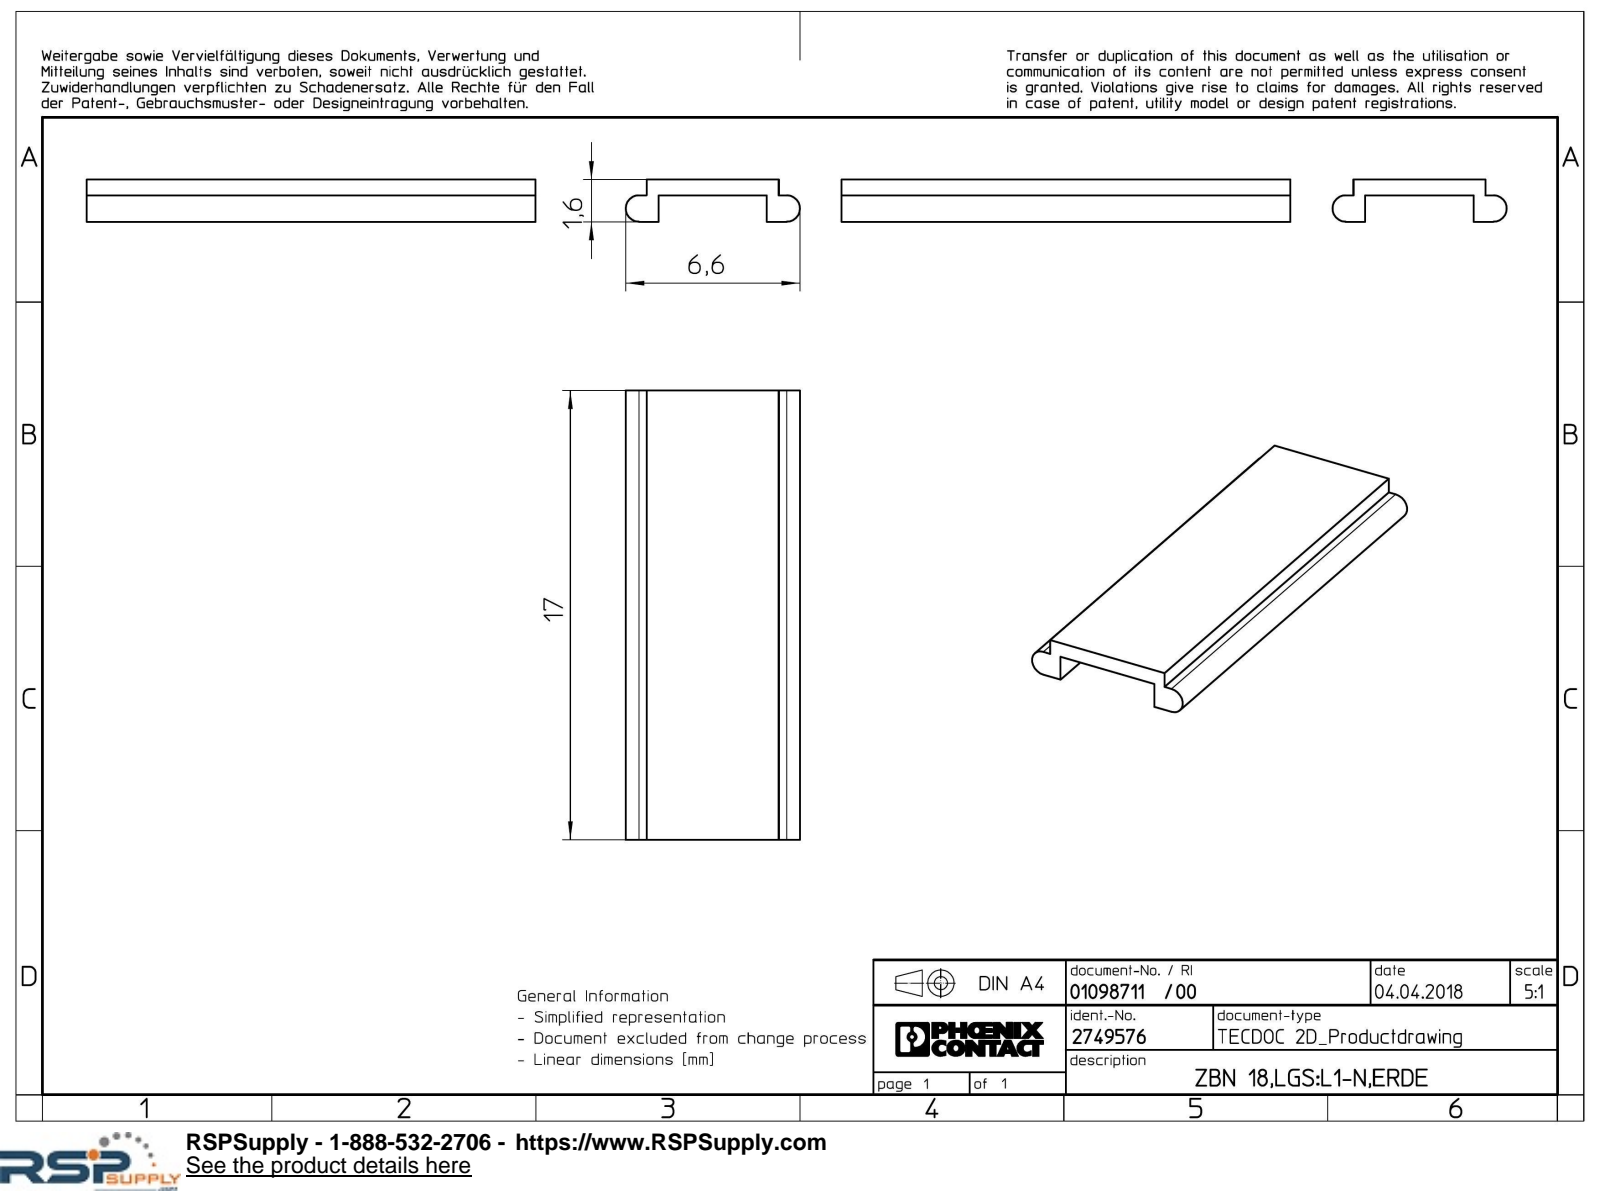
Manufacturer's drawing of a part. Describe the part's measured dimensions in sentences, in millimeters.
The part is named "ZBN_18_UNBEDRUCKT-select". Its 3-D file was written by "Creo Elements/Direct Modeling 20.1A 29-Sep-2018 (C) Parametric Technology GmbH (AUTOMOTIVE_DESIGN)". It is 1 solid with 14 faces: 12 planar, 2 cylindrical and 0 other. Overall it measures 17 by 6.6 by 1.6 millimeters. Its volume is 90 cubic millimeters and its surface area 309 square millimeters. Partial cylindrical surfaces (rounded edges, fillets, slot ends): 2 of radius 0.5. The main face-to-face distances are 0.6, 1, 1.6, 0.45, 4.55, 4.1, 5, 17.
